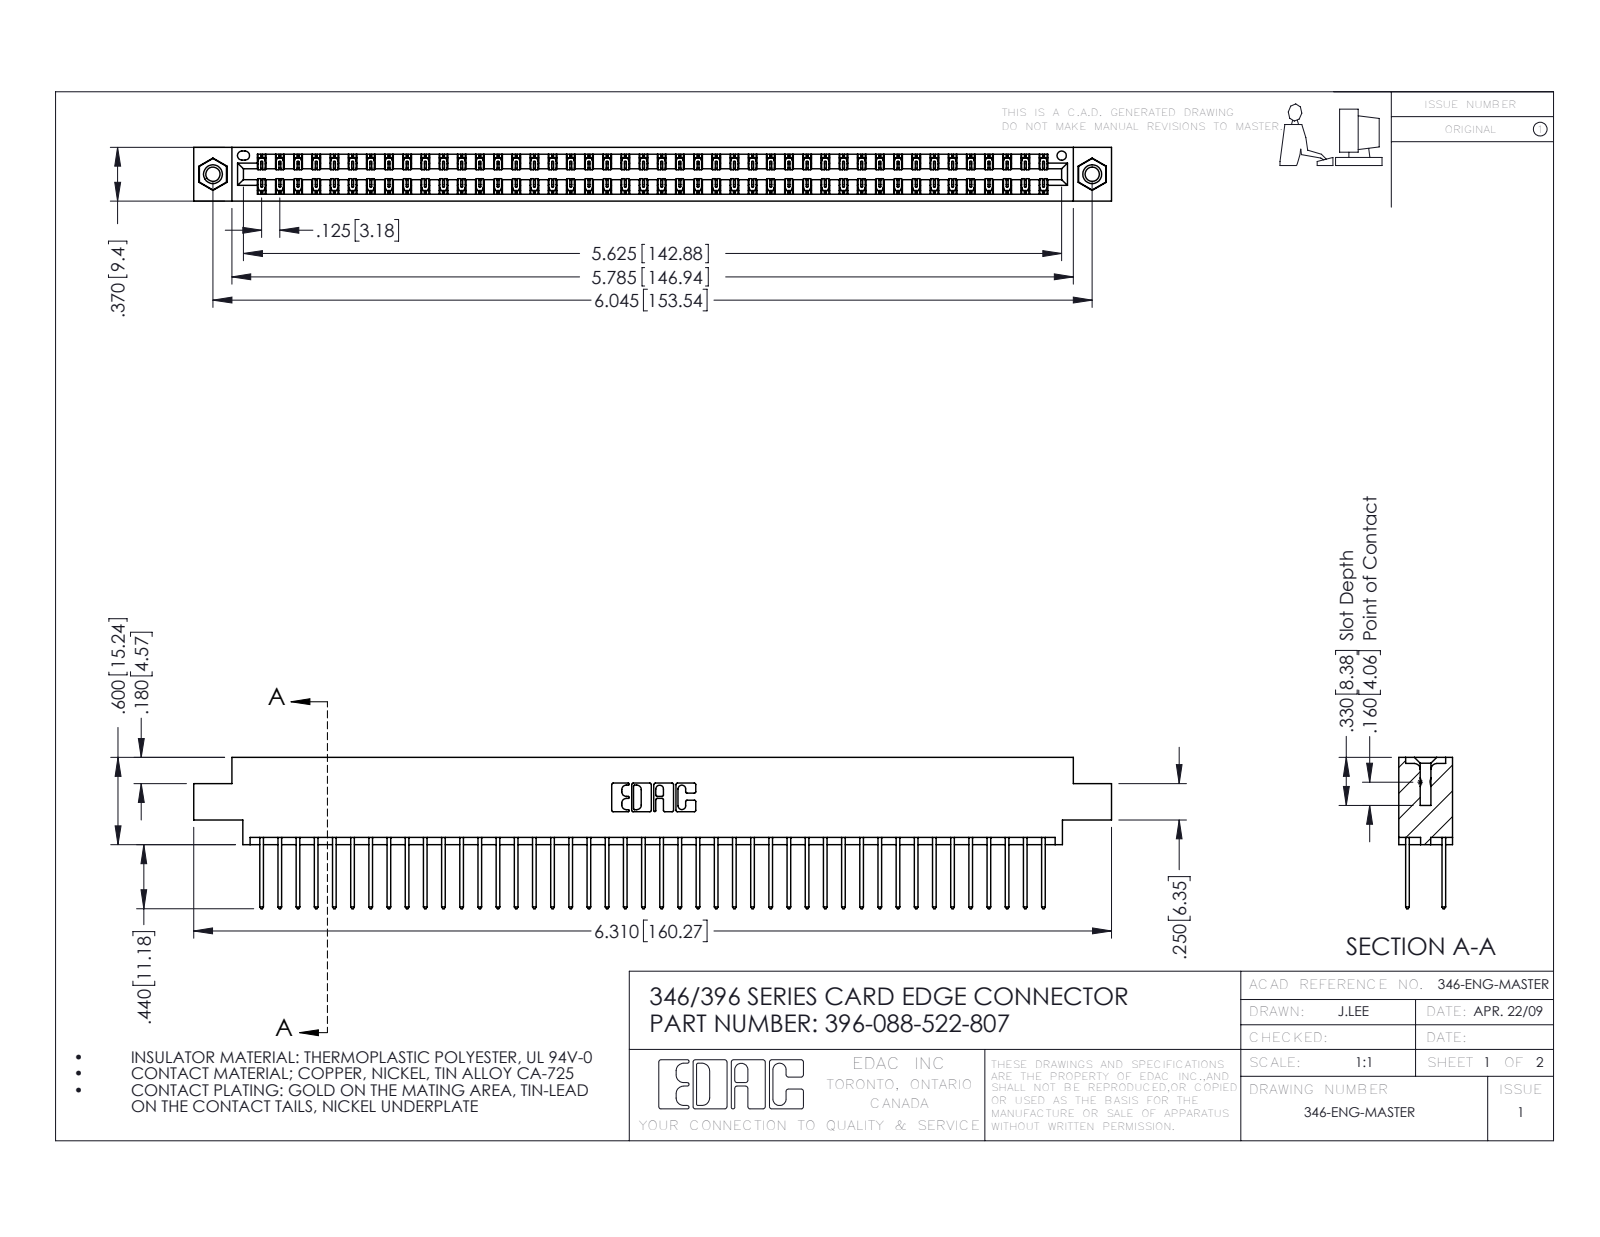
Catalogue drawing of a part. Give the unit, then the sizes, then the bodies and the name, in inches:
Units: inches
Overall size (bounding box): 6.31 × 1.04 × 0.37
Round holes (diameter × count): ⌀0.098 ×2, ⌀0.125 ×2, ⌀0.156 ×2, ⌀0.064 ×1
Round bosses / shafts (diameter × count): ⌀0.155 ×2
Partial cylindrical surfaces — rounded edges, fillets, slot ends (radius × count): R0.006 ×132, R0.01 ×88, R0.01 ×22, R0.007 ×6, R0.031 ×6, R0.026 ×3, R0.014 ×2, R0.022 ×2
Main face-to-face distances: 0.048, 0.322, 0.25, 0.37, 0.072, 0.298, 0.025, 0.275, 0.222, 0.148
Hole centre spacings: 0.246, 5.836, 6.045
Volume: 0.958 in³ · Surface area: 35.45 in²
Bodies: 91 solids, 4762 faces (3192 planar, 1554 cylindrical, 16 other)
Part name (STEP PRODUCT): 345-292-001_345-293-122; 396-088-522-807; 346 Part_0.170 Offset - 0.156 Dia-TI; 345-250-001_345-250-005-103
STEP written by: SolidWorks 2016 (CONFIG_CONTROL_DESIGN)
